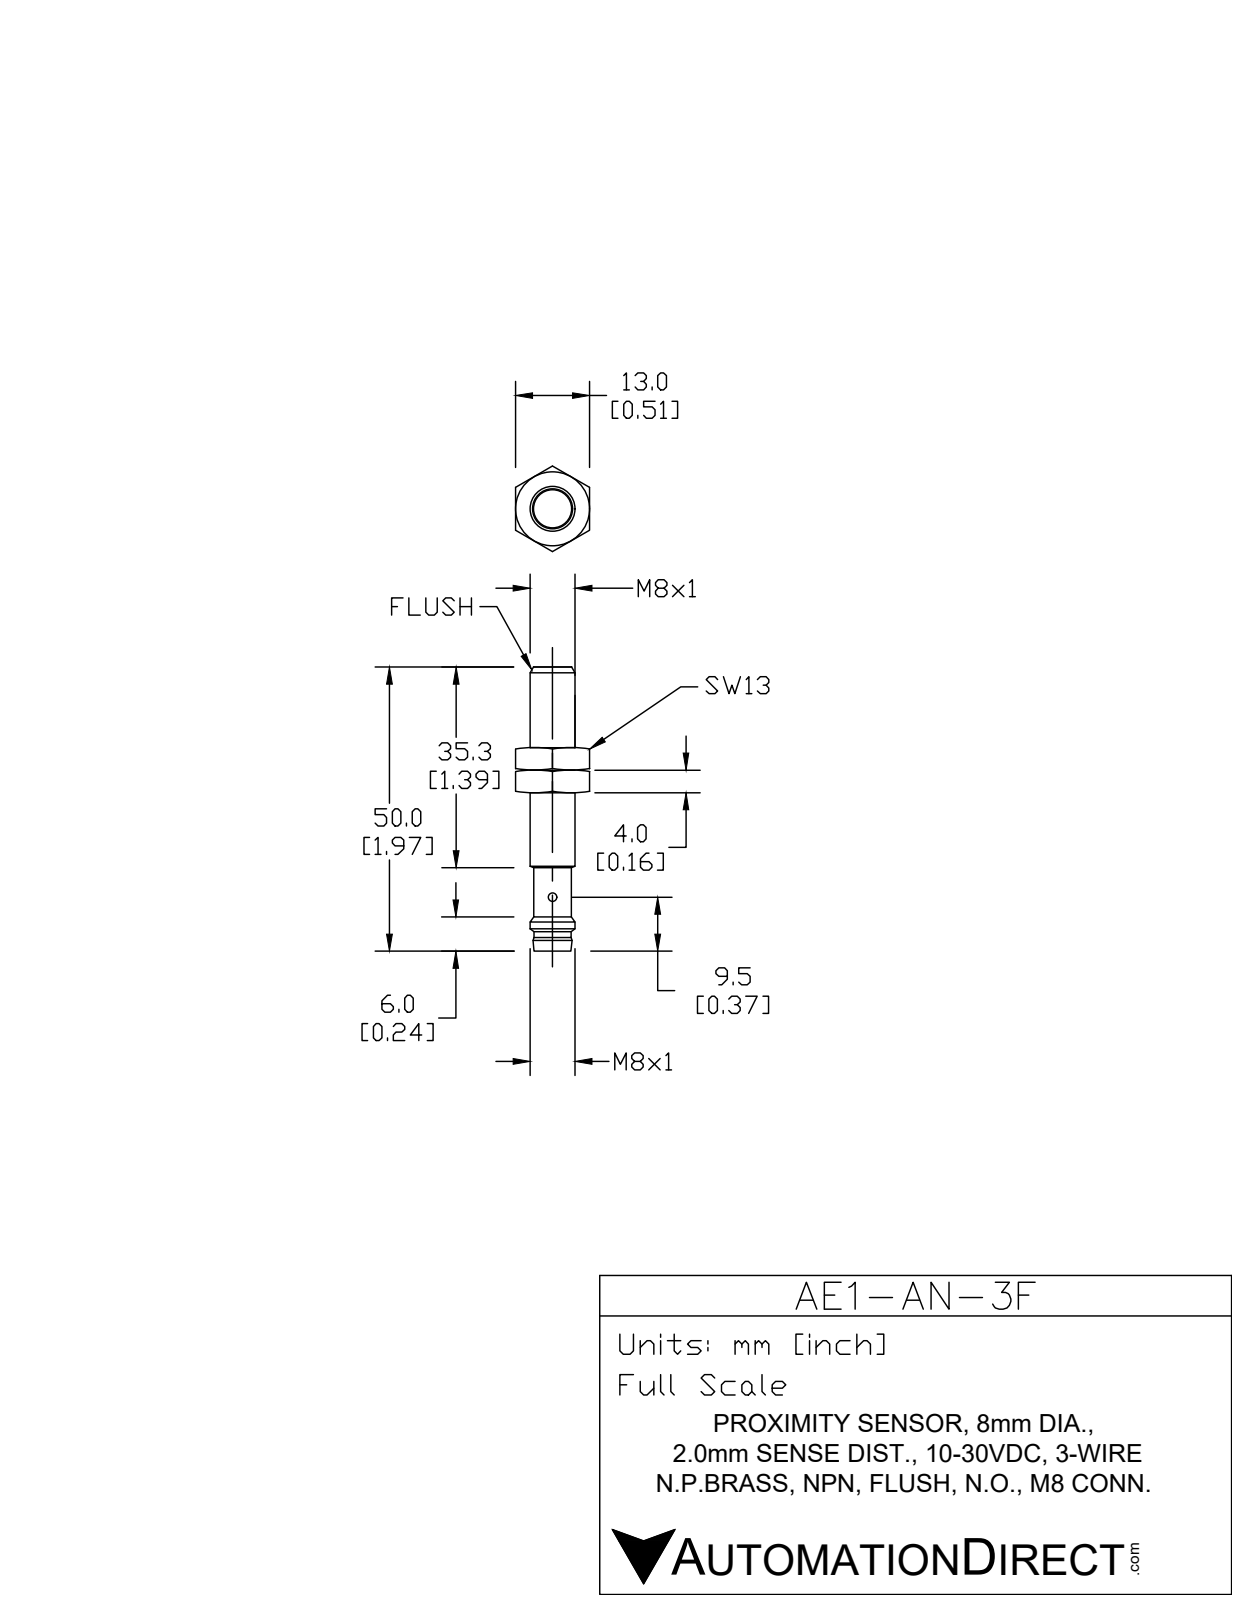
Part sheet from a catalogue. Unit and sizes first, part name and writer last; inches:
Units: inches
Overall size (bounding box): 1.969 × 0.315 × 0.315
Round holes (diameter × count): ⌀0.079 ×2, ⌀0.23 ×1
Round bosses / shafts (diameter × count): ⌀0.039 ×3, ⌀0.315 ×1, ⌀0.272 ×1, ⌀0.256 ×1
Main face-to-face distances: 1.772, 1.783, 1.516, 1.504, 0.268, 1.76, 0.256, 1.969, 1.957, 0.453
Volume: 0.143 in³ · Surface area: 2.594 in²
Bodies: 3 solids, 61 faces (11 planar, 30 cylindrical, 20 other)
Part name (STEP PRODUCT): AE1-AN-3F
STEP written by: SolidWorks 2017 (AUTOMOTIVE_DESIGN)
